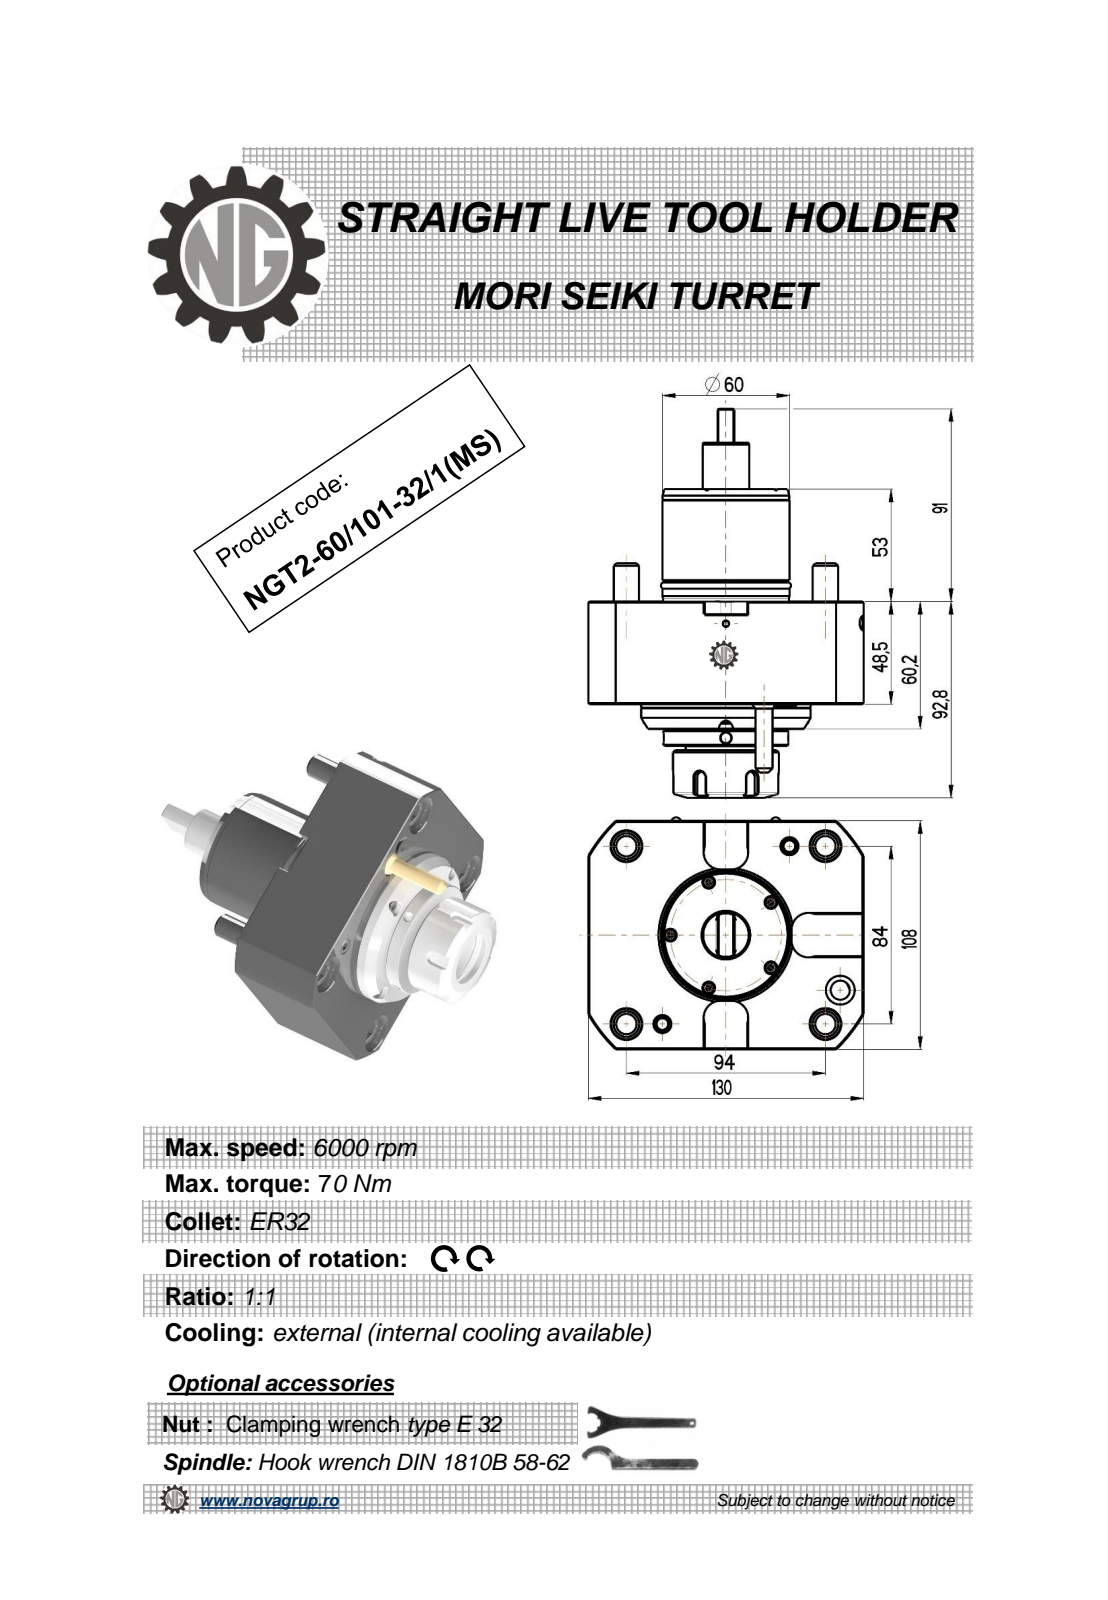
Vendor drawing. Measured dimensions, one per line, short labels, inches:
name: NGT2_60_101_32_1_MS
written by: PRO/ENGINEER BY PARAMETRIC TECHNOLOGY CORPORATION, 2010280 (CONFIG_CONTROL_DESIGN)
unit: in
bodies: 2 solids, 274 faces (94 planar, 81 cylindrical, 99 other)
size: 7.236 × 5.118 × 4.252
volume: 57.43 in³; area: 125.8 in²
holes: 3× ⌀0.197, 1× ⌀0.118, 1× ⌀0.354, 1× ⌀1.063, 1× ⌀1.811
bosses: 4× ⌀0.472, 1× ⌀3.15, 1× ⌀2.362, 1× ⌀2.354, 1× ⌀2.339, 1× ⌀2.323, 1× ⌀2.181, 1× ⌀1.969
rounds: 6× R0.009, 6× R0.315, 5× R0.118, 4× R0.138, 2× R0.031, 1× R0.423, 1× R2.953
face distances: 1.909, 4.252, 5.118, 2.37, 0.461, 2.087, 3.996, 4.457, 0.236, 0.315
hole spacings: 1.567, 1.835, 2.359
